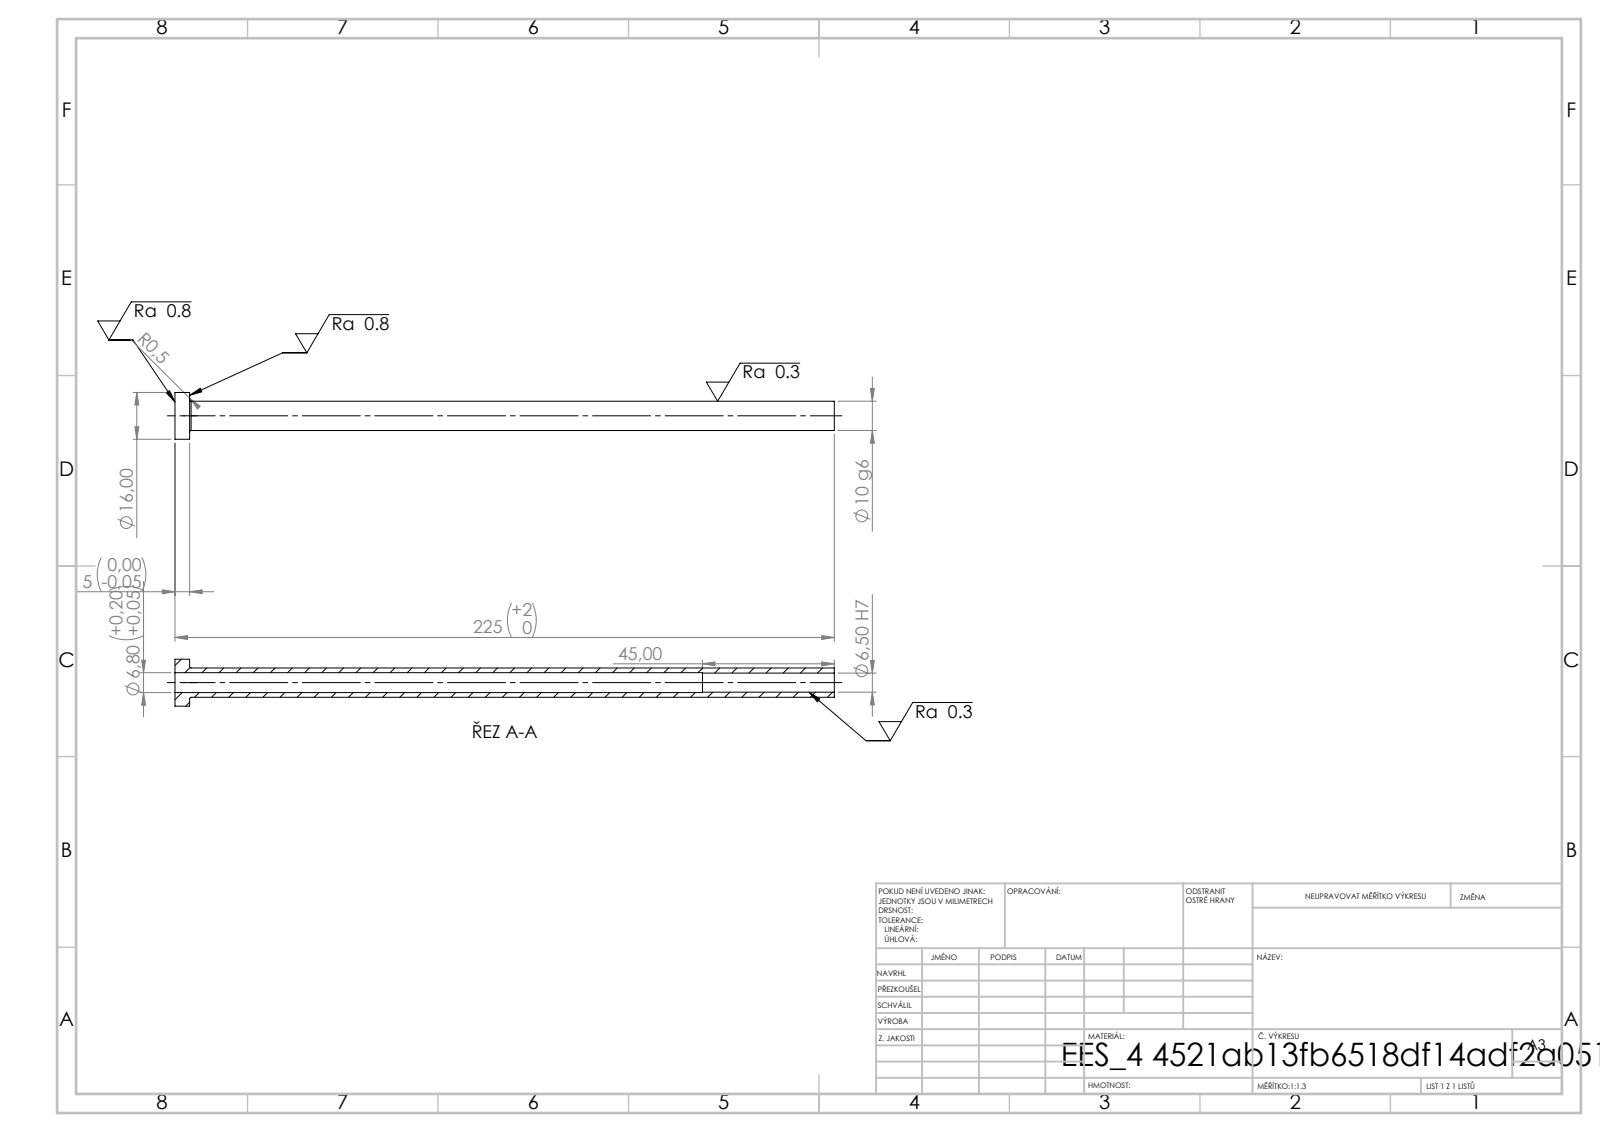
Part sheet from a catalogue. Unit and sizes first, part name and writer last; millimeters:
Units: millimetres
Overall size (bounding box): 225 × 16 × 16
Round holes (diameter × count): ⌀6.5 ×1, ⌀6.8 ×1
Round bosses / shafts (diameter × count): ⌀16 ×1, ⌀10 ×1
Main face-to-face distances: 5, 225, 220, 180, 175, 45
Volume: 10 256 mm³ · Surface area: 12 256 mm²
Bodies: 1 solid, 14 faces (4 planar, 8 cylindrical, 2 other)
STEP written by: SolidWorks 2019 (CONFIG_CONTROL_DESIGN)
